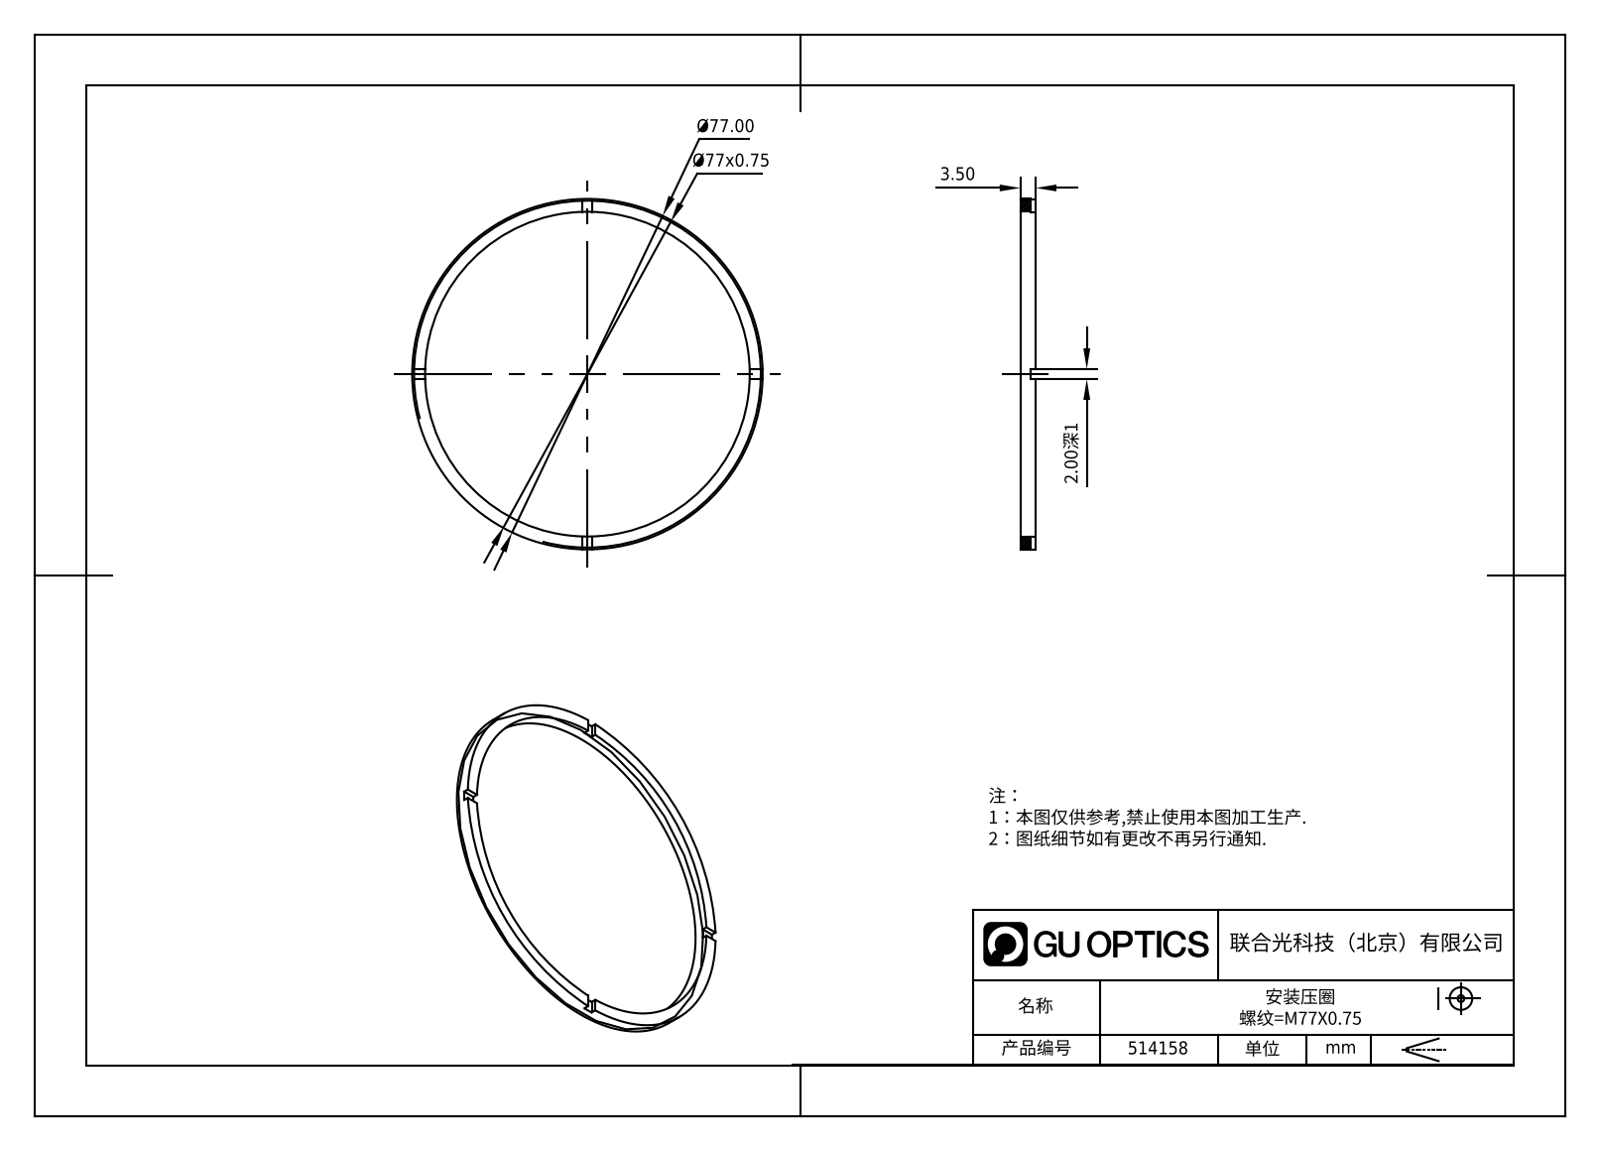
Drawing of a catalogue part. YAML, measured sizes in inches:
part_name: "514158"
step_written_by: "SolidWorks 2020 (CONFIG_CONTROL_DESIGN)"
units: inches
bodies: {solids: 1, faces: 21, planar: 17, cylindrical: 4, other: 0}
overall_size: [3.031, 3.031, 0.138]
volume: 0.147
surface_area: 4.697
round_holes:
  - {diameter: 2.795, count: 1}
round_bosses_or_shafts:
  - {diameter: 3.031, count: 1}
face_to_face_distances: [0.138, 0.098, 0.039, 0.079]
